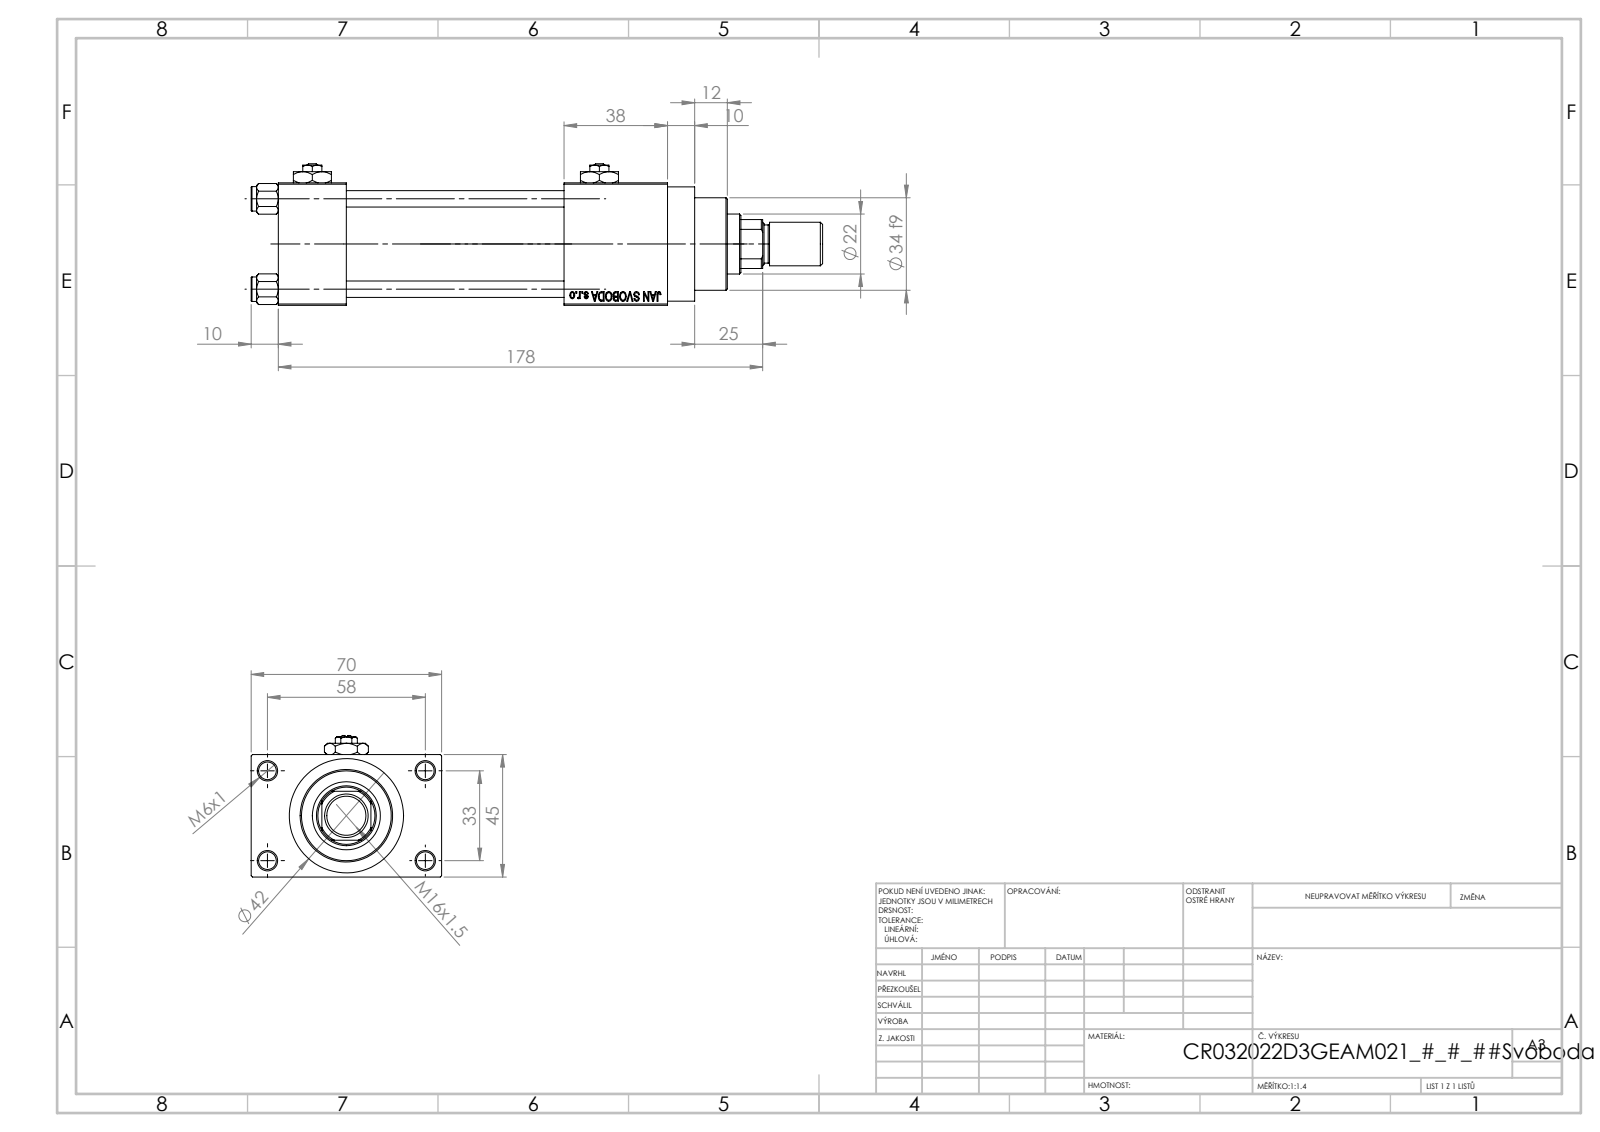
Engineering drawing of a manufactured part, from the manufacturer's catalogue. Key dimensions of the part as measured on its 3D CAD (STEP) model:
Part name (STEP PRODUCT): ROD_END_AH; V215_VC_A; V215CR_VCP_D; NUT_M5_D (+3 more)
STEP written by: SolidWorks 2019 (CONFIG_CONTROL_DESIGN)
Units: millimetres
Bodies: 14 solids, 1216 faces (546 planar, 104 cylindrical, 566 other)
Overall size (bounding box): 210 × 70 × 52
Volume: 272 370 mm³ · Surface area: 93 674 mm²
Round holes (diameter × count): ⌀6 ×4, ⌀6.5 ×4, ⌀7 ×2, ⌀13.16 ×2, ⌀20 ×2, ⌀10.5 ×1, ⌀22 ×1, ⌀24 ×1, ⌀25 ×1, ⌀32 ×1, ⌀33 ×1
Round bosses / shafts (diameter × count): ⌀9 ×4, ⌀42 ×1, ⌀38 ×1, ⌀34 ×1, ⌀16 ×1, ⌀14 ×1
Partial cylindrical surfaces — rounded edges, fillets, slot ends (radius × count): R10.5 ×1
Main face-to-face distances: 45, 25, 12.5, 57.5, 80, 105, 118, 70, 38, 143
Hole centre spacings: 12.4, 23.48, 33.2, 33.37, 35.35, 45.6, 56.35, 33
